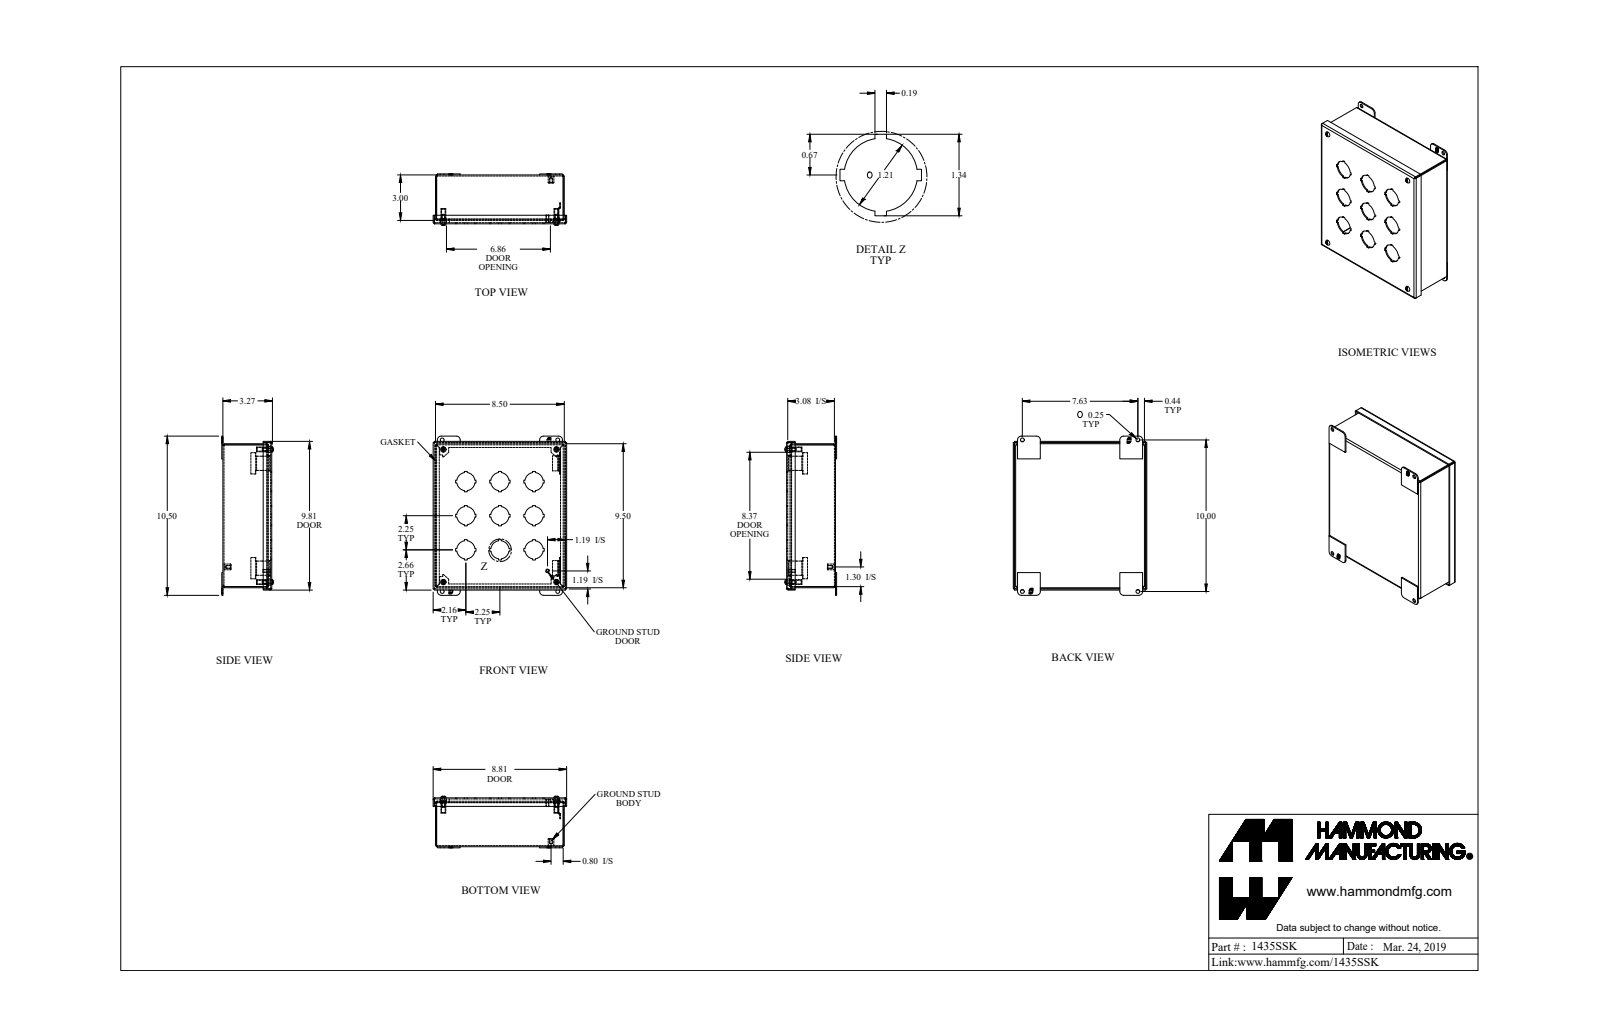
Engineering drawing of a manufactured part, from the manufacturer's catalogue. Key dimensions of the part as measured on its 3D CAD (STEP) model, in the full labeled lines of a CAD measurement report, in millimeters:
Part name (STEP PRODUCT): 1435SSK_Default
STEP written by: SolidWorks 2019 (CONFIG_CONTROL_DESIGN)
Units: millimetres
Bodies: 23 solids, 749 faces (531 planar, 188 cylindrical, 30 other)
Overall size (bounding box): 266.7 × 223.8 × 86.5
Volume: 406 600 mm³ · Surface area: 425 000 mm²
Round holes (diameter × count): ⌀30.7 ×9, ⌀6.4 ×8, ⌀1.7 ×4, ⌀6.1 ×4, ⌀6.4 ×4, ⌀10.3 ×4, ⌀4 ×1
Round bosses / shafts (diameter × count): ⌀4.8 ×5, ⌀10.3 ×4, ⌀8 ×4, ⌀3.8 ×4, ⌀9.5 ×1, ⌀6.4 ×1
Partial cylindrical surfaces — rounded edges, fillets, slot ends (radius × count): R0.9 ×12, R2.7 ×12, R6.4 ×8, R0.7 ×4, R2.2 ×4, R4.3 ×4
Main face-to-face distances: 1.8, 80, 81.8, 78.2, 214.1, 239.5, 3.9, 215.9, 212.2, 241.3
Hole centre spacings: 57.2, 80.8, 127.8, 189.5, 189.5, 192.3, 16, 114.3
